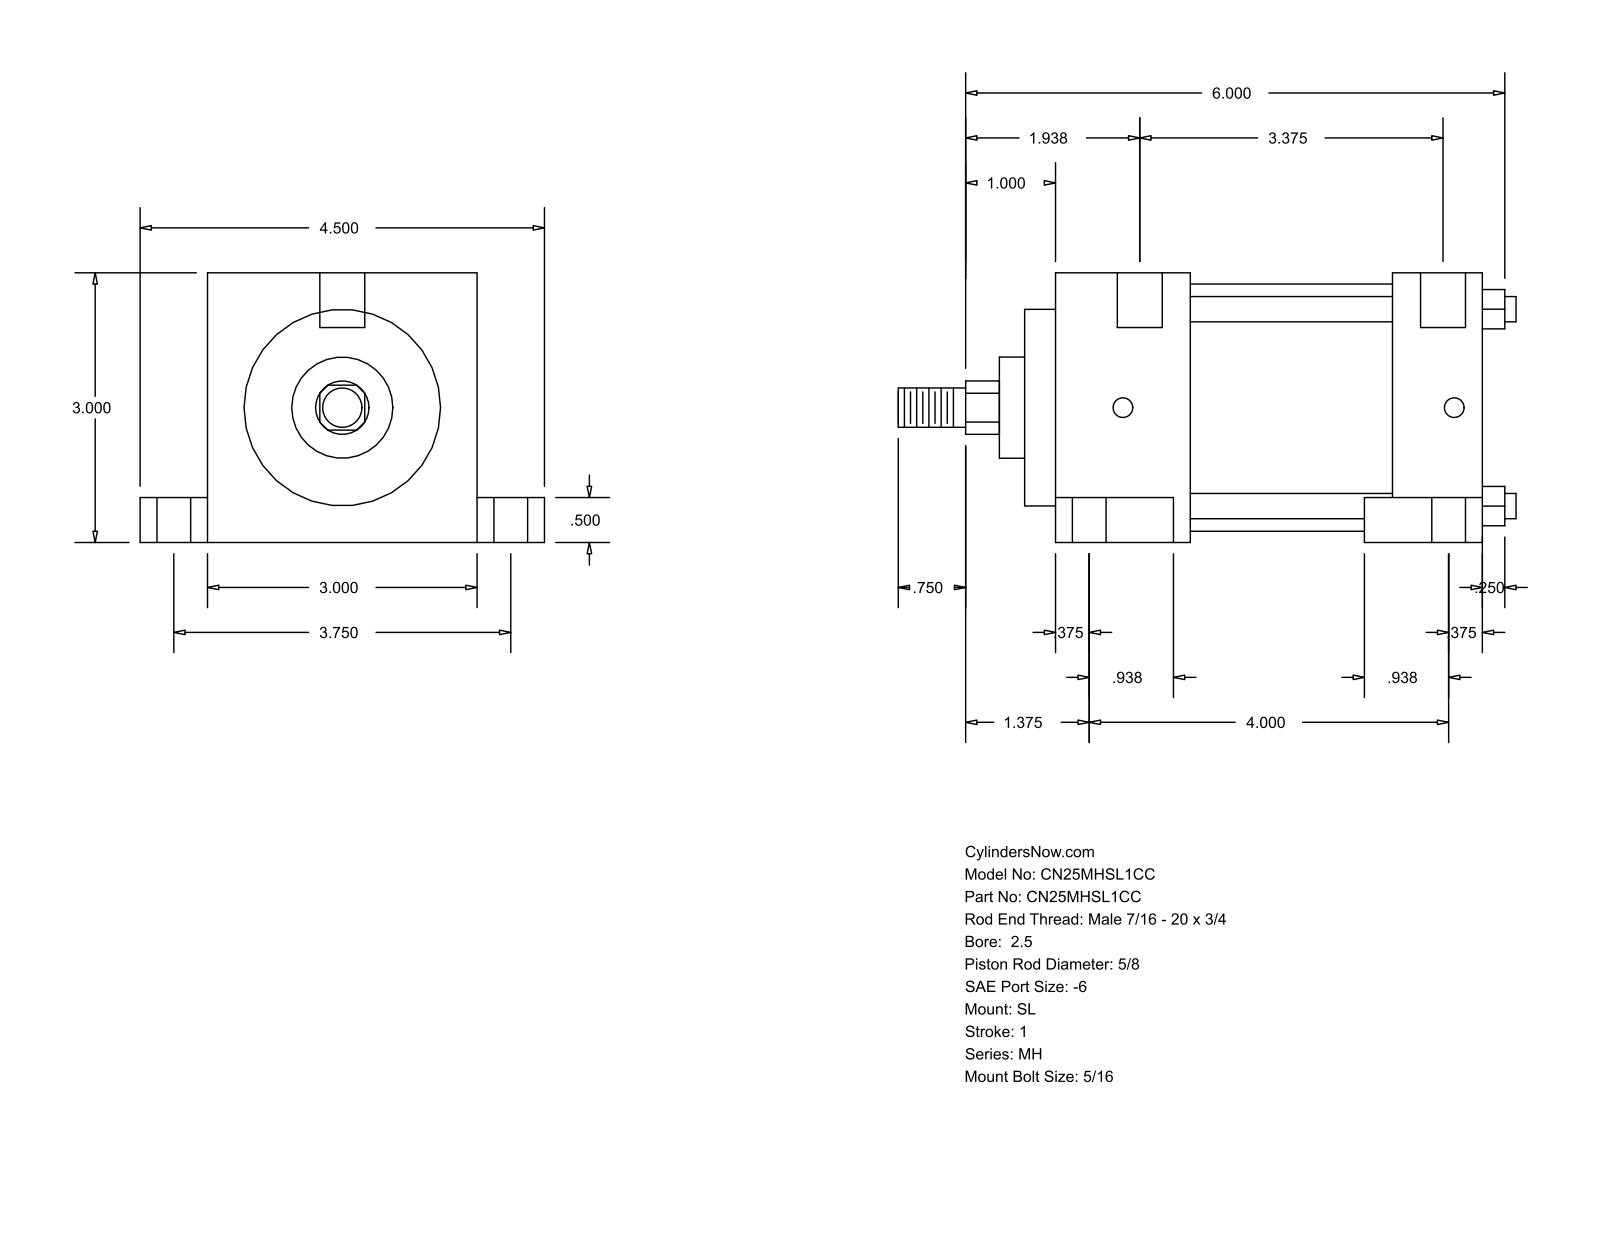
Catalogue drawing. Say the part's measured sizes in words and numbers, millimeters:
The part is named "MH_SL__0250_0.625". Its 3-D file was written by "GSSL Pune (CONFIG_CONTROL_DESIGN)". It is 0 solids with 86 faces: 61 planar, 25 cylindrical and 0 other. Overall it measures 174.62 by 114.3 by 76.2 millimeters. Round holes: 2 of diameter 5.56, 2 of diameter 9.53, 2 of diameter 15.88, 1 of diameter 12.7. Round bosses or shafts: 4 of diameter 7.14, 1 of diameter 69.85, 1 of diameter 55.55, 1 of diameter 28.57, 1 of diameter 15.88, 1 of diameter 11.11. Partial cylindrical surfaces (rounded edges, fillets, slot ends): 1 of radius 7.54. The main face-to-face distances are 76.2, 25.4, 103.98, 129.38, 63.5, 12.7, 19.05, 95.25, 31.75, 96.04. The hole center spacings are 47.65, 3.17, 95.24.
